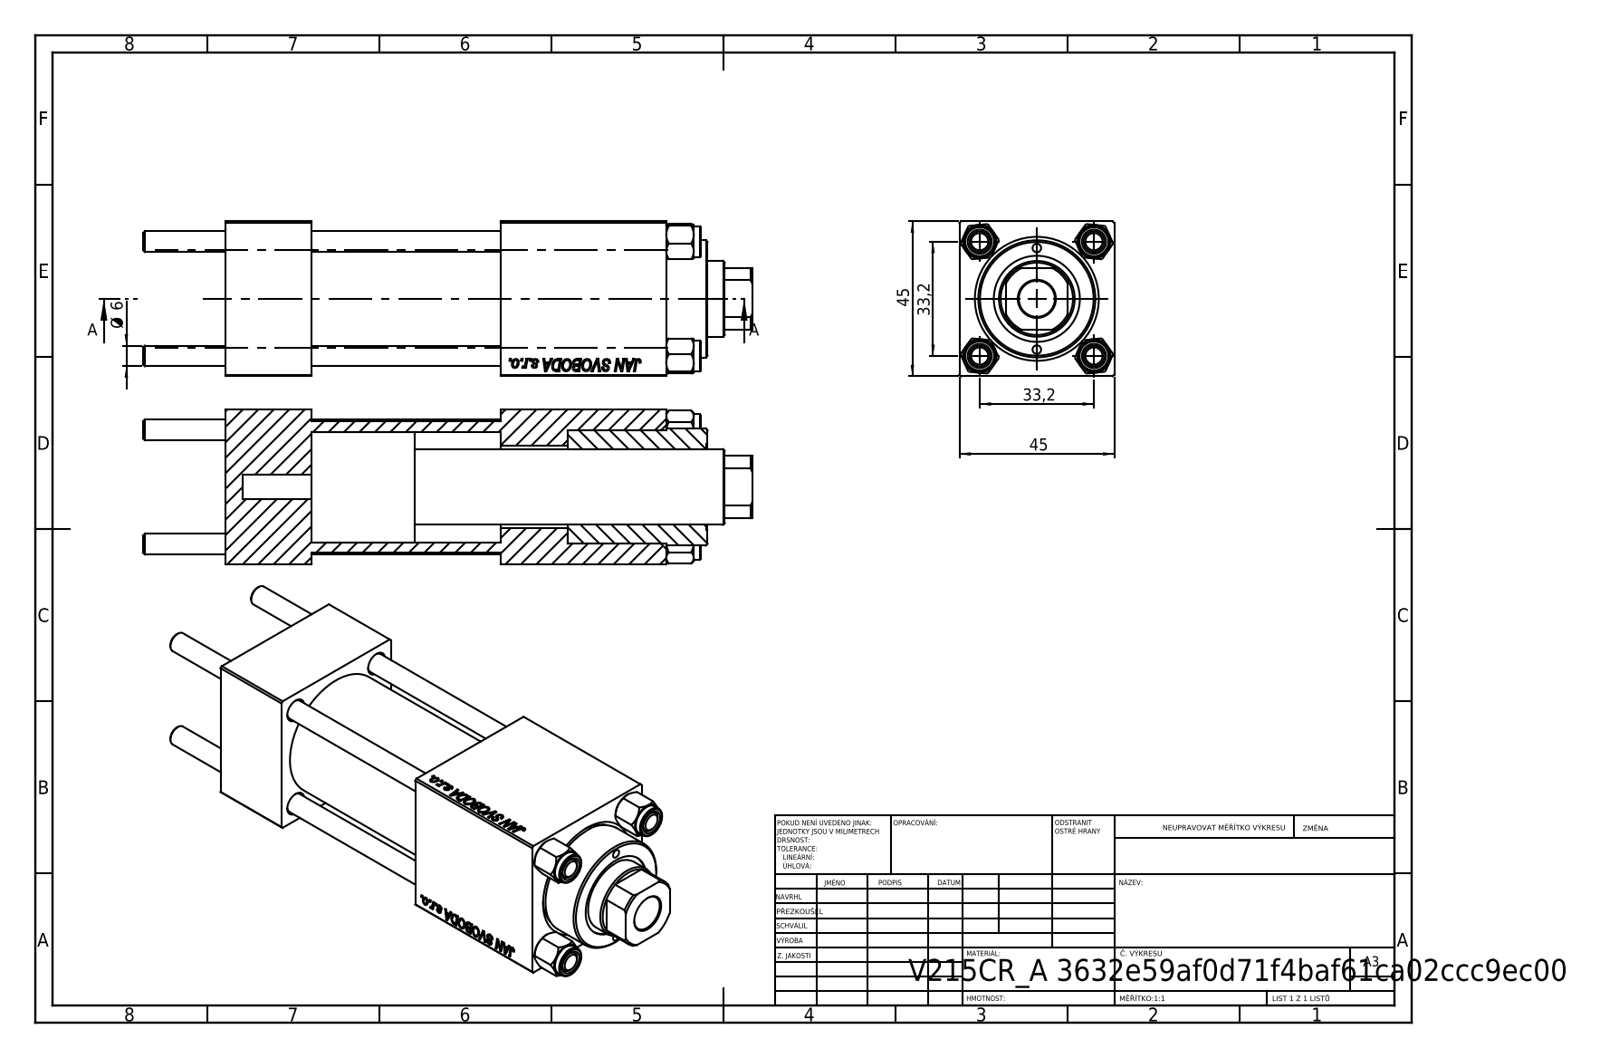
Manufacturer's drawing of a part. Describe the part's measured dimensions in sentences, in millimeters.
The part is named "V215CR_VCP; V215CR_BODY_A; NUT_M5; CR025_012_A_0_G_A_G_M_020_+#_##_TYCINKA (+1 more)". Its 3-D file was written by "SolidWorks 2019 (CONFIG_CONTROL_DESIGN)". It is 11 solids with 1139 faces: 521 planar, 82 cylindrical and 536 other. Overall it measures 177 by 45 by 45 millimeters. Its volume is 218 223 cubic millimeters and its surface area 79 131 square millimeters. Round holes: 4 of diameter 6, 2 of diameter 2.5, 2 of diameter 7, 2 of diameter 13.16, 2 of diameter 20, 1 of diameter 10.5, 1 of diameter 22, 1 of diameter 24, 1 of diameter 25, 1 of diameter 32, 1 of diameter 33. Round bosses or shafts: 4 of diameter 9, 1 of diameter 38, 1 of diameter 34. Partial cylindrical surfaces (rounded edges, fillets, slot ends): 1 of radius 10.5. The main face-to-face distances are 45, 25, 55, 128, 80, 103, 48, 99.3, 74.3, 19.3. The hole center spacings are 16.7, 23.48, 33.2, 35.47, 14.75, 46.95, 29.5, 80.5.
